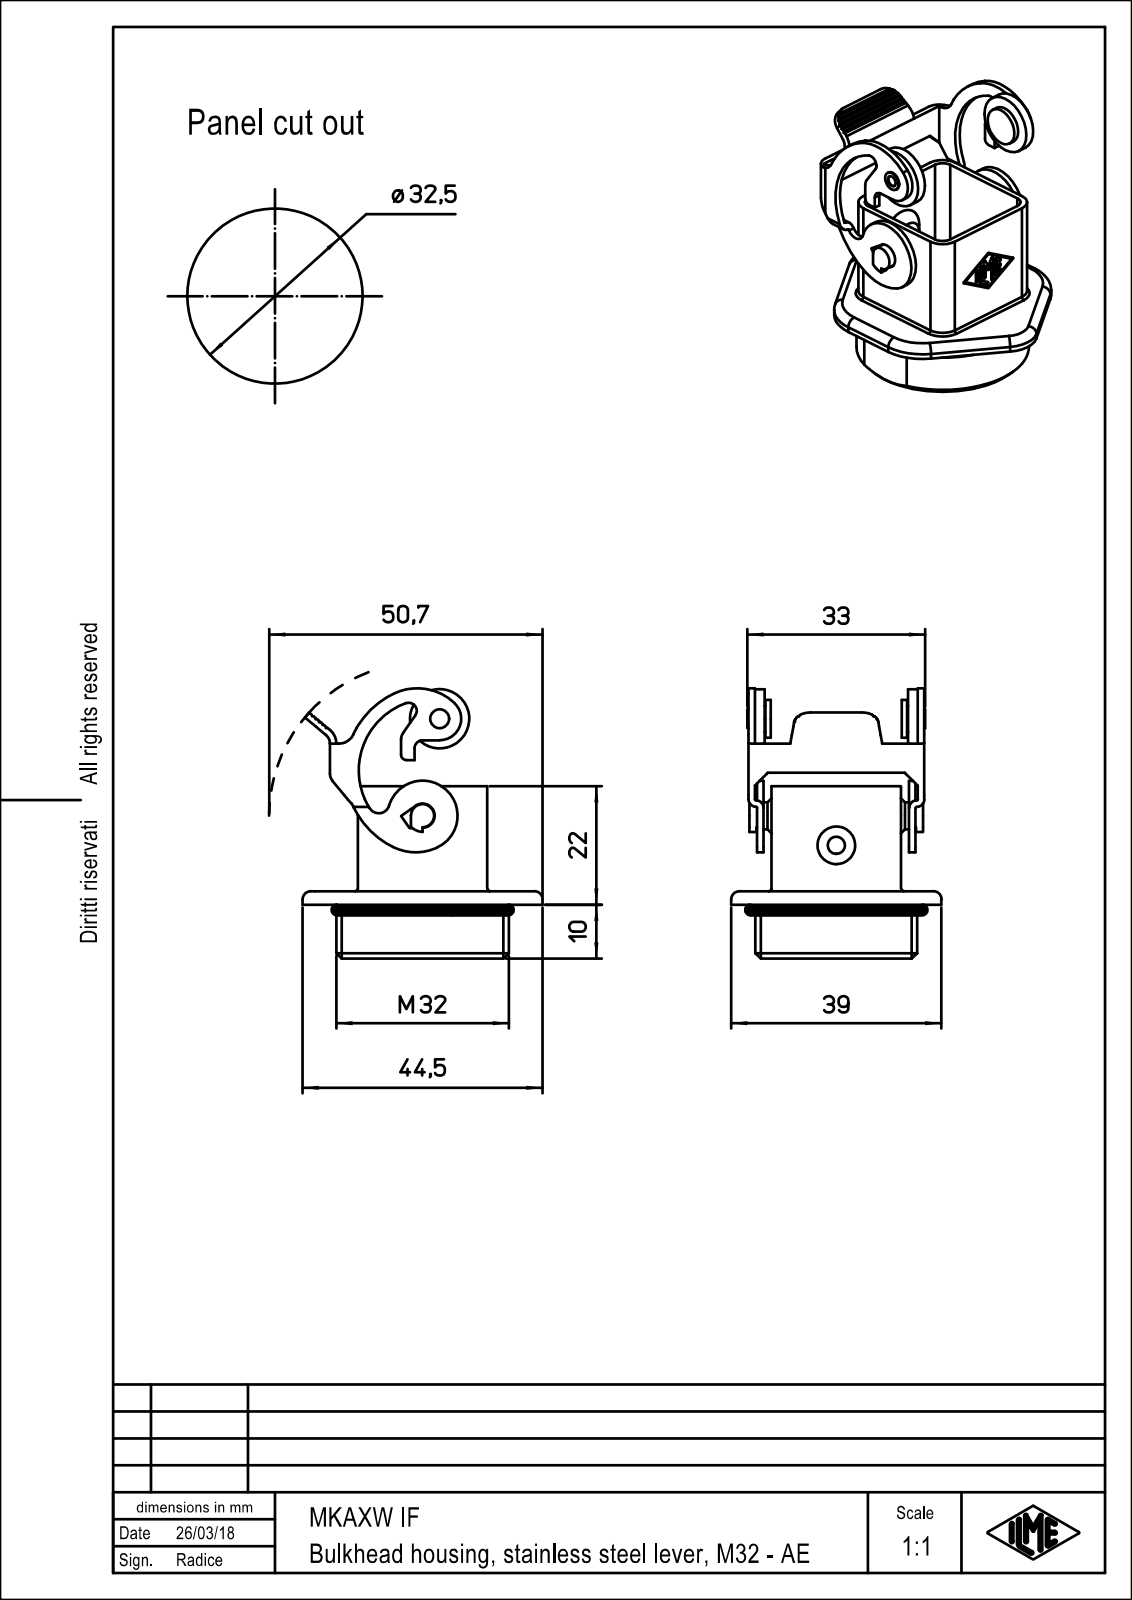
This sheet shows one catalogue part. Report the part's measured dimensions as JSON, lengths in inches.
{"part_name": "MKAXW_IF", "step_written_by": "PTC Creo Elements/Direct Modeling 19.0E 27-Jun-2016 (C) Parametric Technology GmbH (AUTOMOTIVE_DESIGN)", "units": "inches", "bodies": {"solids": 1, "faces": 246, "planar": 114, "cylindrical": 110, "other": 22}, "overall_size": [1.975, 1.752, 1.535], "volume_in3": 0.591, "surface_area_in2": 16.88, "round_holes": [[0.079, 1], [0.126, 1], [0.276, 1]], "round_bosses_or_shafts": [[1.173, 1], [0.433, 1], [0.276, 1], [0.197, 1], [0.189, 1], [0.169, 1], [0.138, 1]], "partial_cylinders_radius": [[0.059, 8], [0.079, 8], [0.118, 5], [0.126, 5], [0.008, 4], [0.02, 4], [0.055, 4], [0.354, 4]], "face_to_face_distances": [0.047, 0.945, 0.063, 1.173, 0.098, 0.059, 1.114, 1.102, 0.051, 0.118]}
